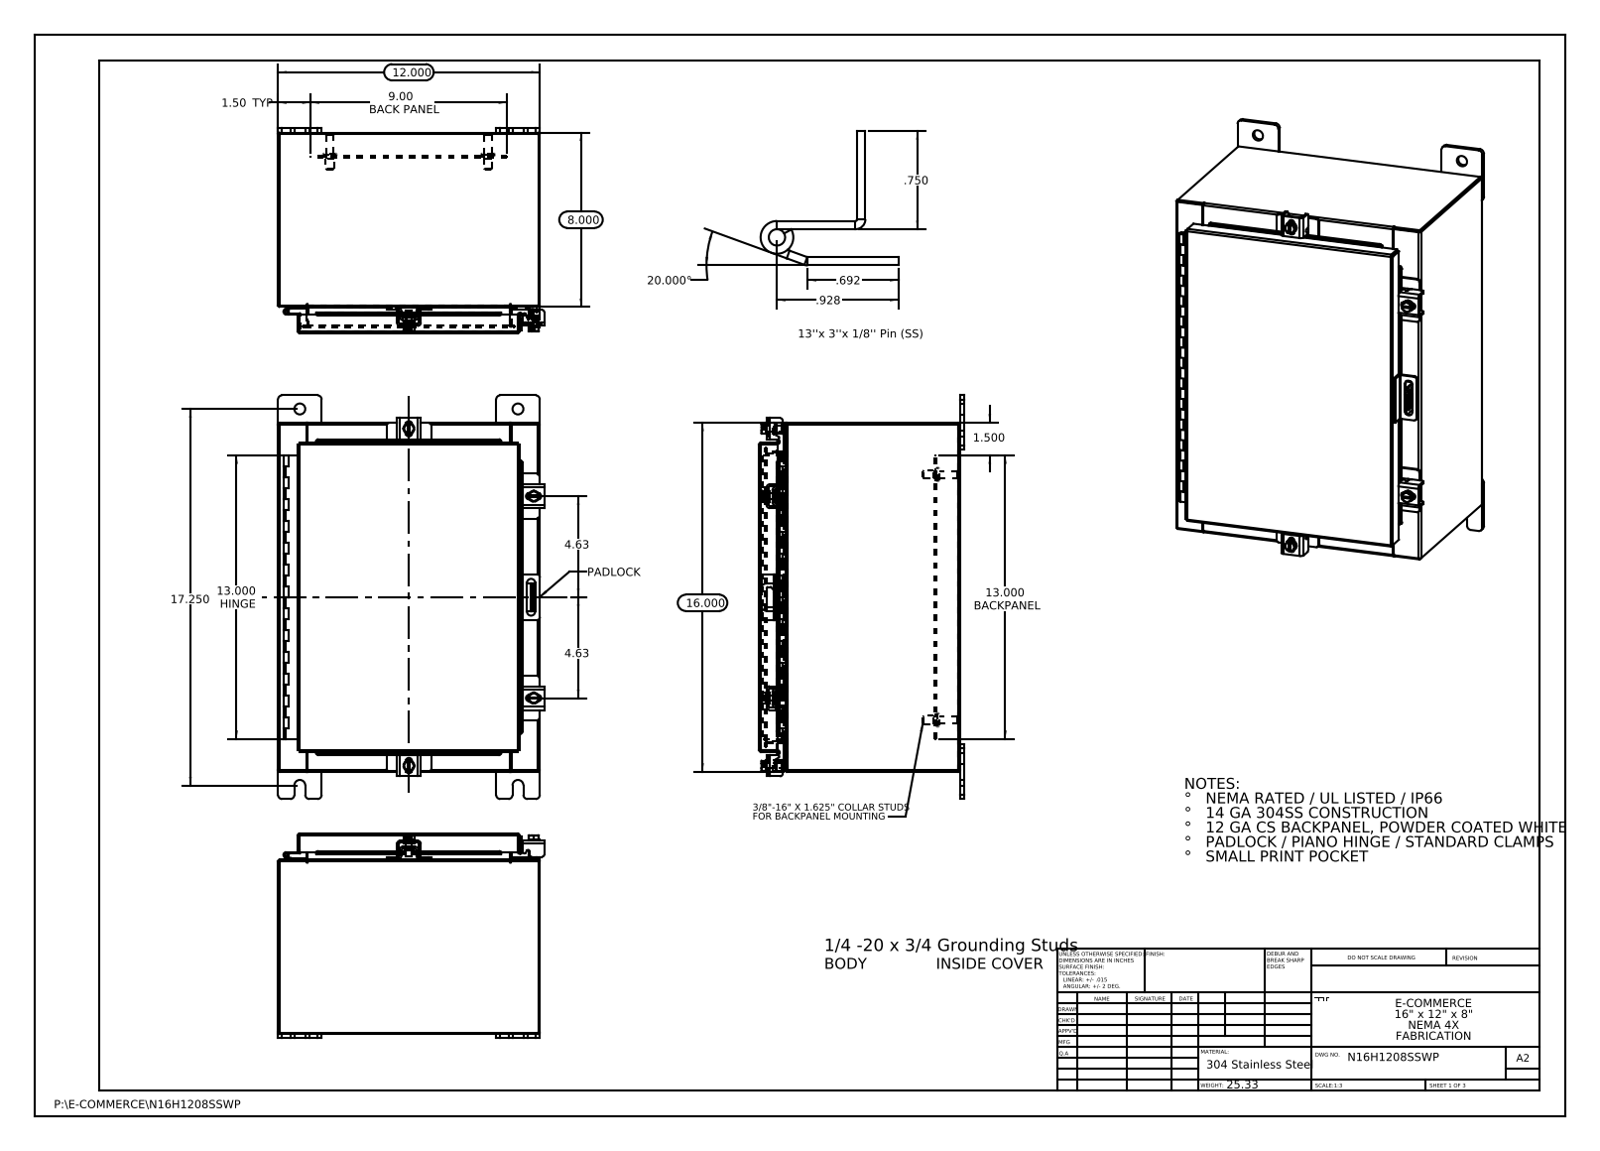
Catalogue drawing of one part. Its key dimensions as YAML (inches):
part_name: "N16H1208SSWP Padlock Hasp; N16H1208SSWP 22104005_DEFAULT; N16H1208SSWP Clamp Bracket; N16H1208SSWP 22101002 (+8 more)"
step_written_by: "SolidWorks 2013 (CONFIG_CONTROL_DESIGN)"
units: inches
bodies: {solids: 37, faces: 1267, planar: 680, cylindrical: 507, other: 80}
overall_size: [18.5, 12.211, 9.389]
volume: 89.65
surface_area: 2294
round_holes:
  - {diameter: 0.5, count: 8}
  - {diameter: 0.213, count: 4}
  - {diameter: 0.26, count: 4}
  - {diameter: 0.125, count: 2}
  - {diameter: 0.125, count: 1}
round_bosses_or_shafts:
  - {diameter: 0.25, count: 5}
  - {diameter: 0.625, count: 4}
  - {diameter: 0.5, count: 4}
  - {diameter: 0.399, count: 4}
  - {diameter: 0.375, count: 4}
  - {diameter: 0.33, count: 4}
partial_cylinders:
  - {radius: 0.19, count: 24}
  - {radius: 0.013, count: 23}
  - {radius: 0.06, count: 22}
  - {radius: 0.088, count: 21}
  - {radius: 0.125, count: 10}
  - {radius: 0.12, count: 8}
  - {radius: 0.141, count: 8}
  - {radius: 0.05, count: 7}
face_to_face_distances: [0.075, 9.126, 11.925, 15.925, 9.201, 9.051, 7.925, 1.201, 11.85, 12]
hole_center_spacings: [13.834, 2.225, 2.327, 3.3, 4.189, 4.19, 5.012, 5.08]
